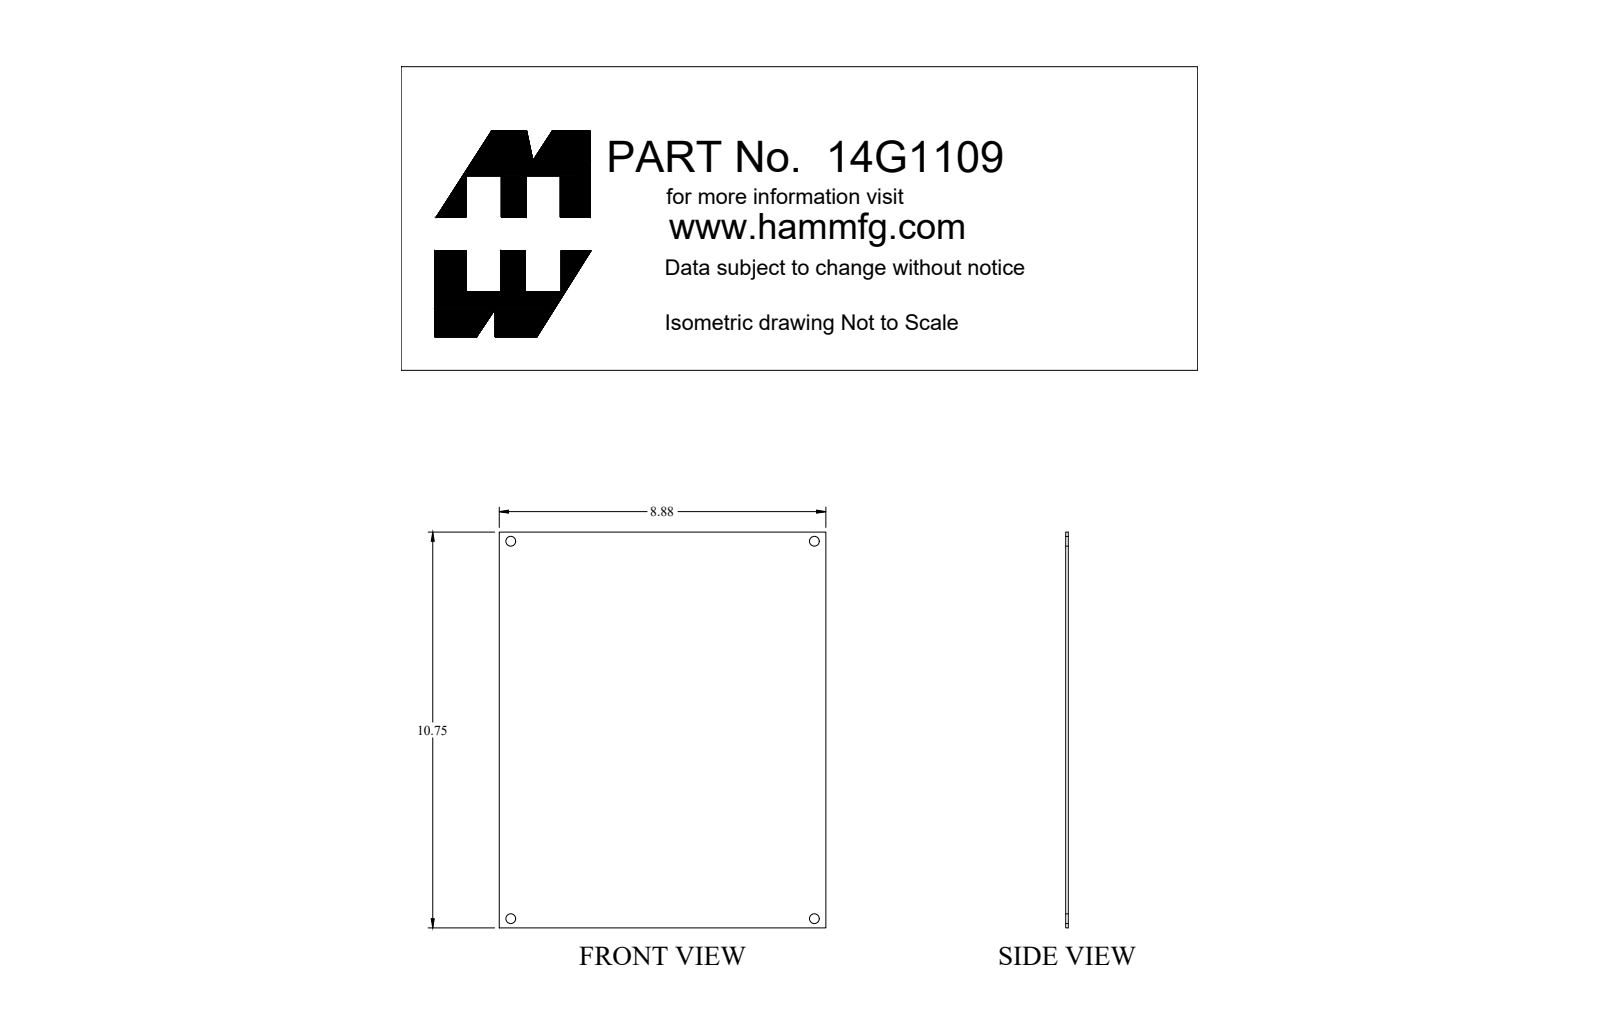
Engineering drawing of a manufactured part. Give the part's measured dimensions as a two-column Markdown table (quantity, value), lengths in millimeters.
| quantity | value |
| --- | --- |
| part name | 14G1109 |
| STEP written by | SolidWorks 2018 (AUTOMOTIVE_DESIGN) |
| units | millimeters |
| bodies | 1 solid, 10 faces (6 planar, 4 cylindrical, 0 other) |
| overall size | 273.1 × 225.4 × 1.8 |
| volume | 112 300 mm³ |
| surface area | 124 800 mm² |
| round holes (diameter × count) | 6.7 × 4 |
| main face-to-face distances | 1.8, 225.4, 273.1 |
| hole center spacings | 209.6, 260.4, 334.2 |
